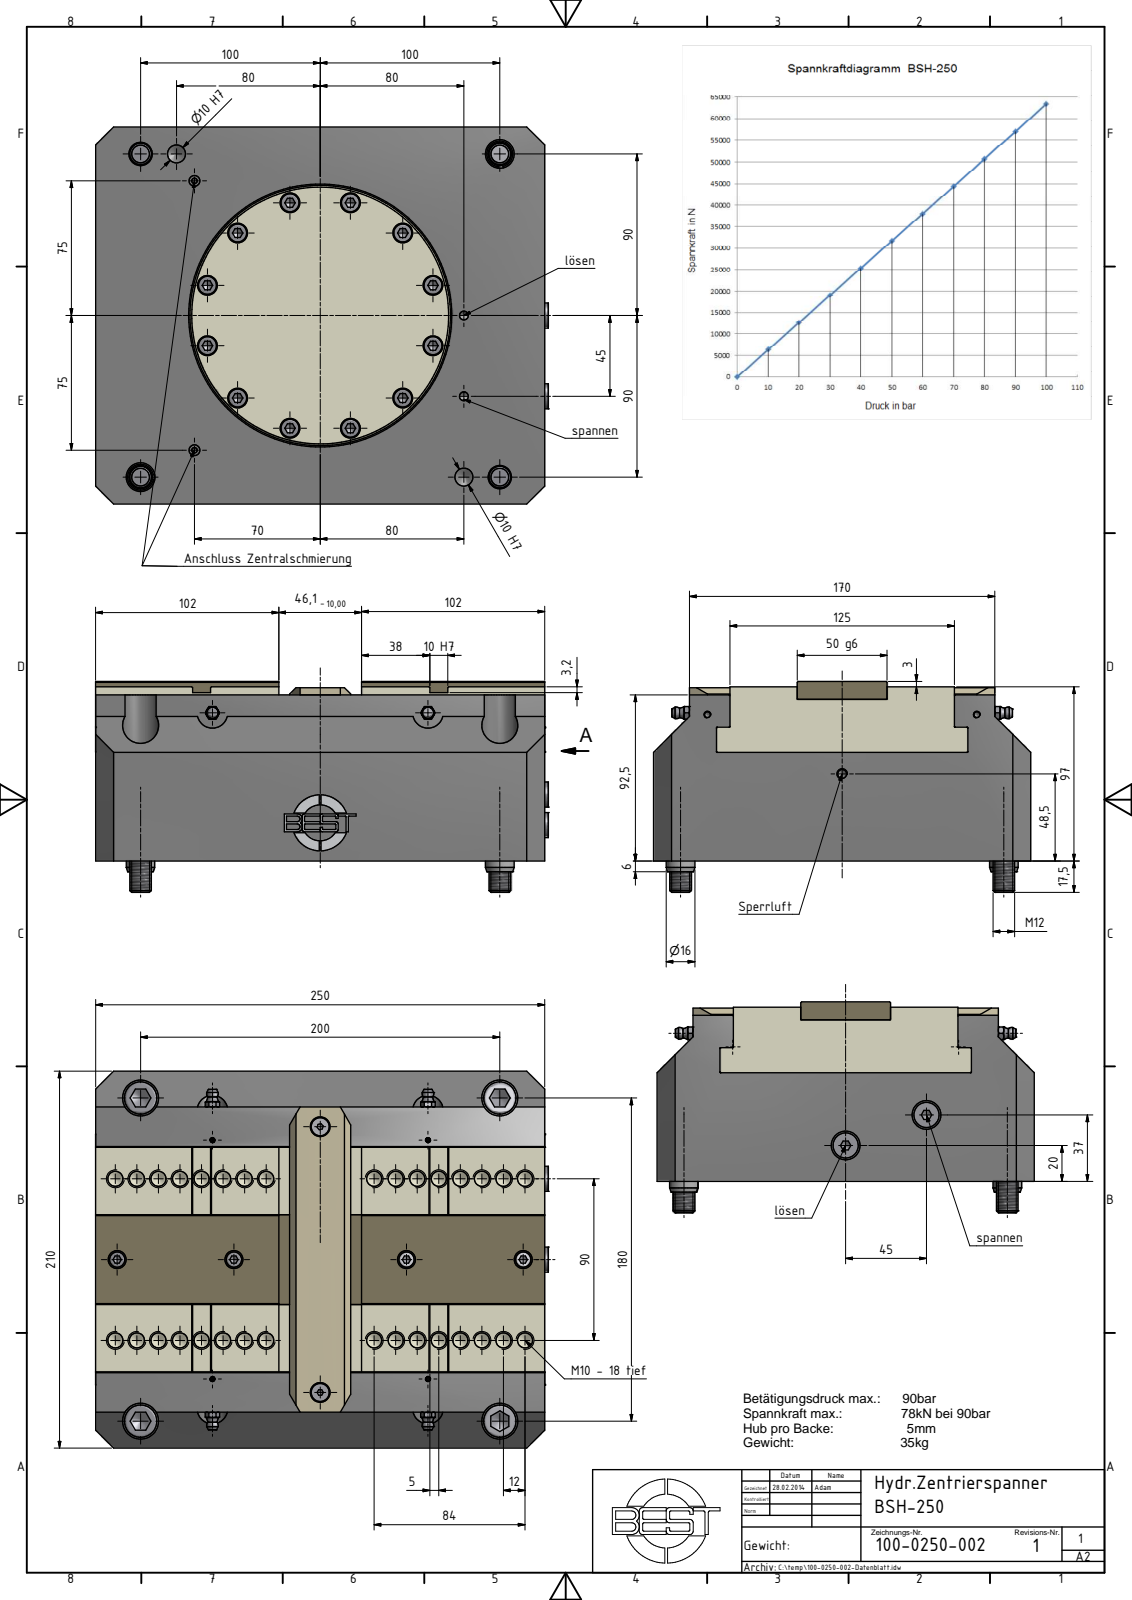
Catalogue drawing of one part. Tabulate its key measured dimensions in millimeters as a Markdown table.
| quantity | value |
| --- | --- |
| part name | 100-0250-002-Kd |
| STEP written by | Autodesk Inventor 2013 (AUTOMOTIVE_DESIGN) |
| units | millimeters |
| bodies | 1 solid, 634 faces (348 planar, 153 cylindrical, 133 other) |
| overall size | 252.54 × 210 × 117.5 |
| volume | 4 651 000 mm³ |
| surface area | 256 629 mm² |
| round holes (diameter × count) | 8.38 × 32, 4.92 × 5, 13 × 4, 16 × 4, 20 × 4, 3 × 2, 6 × 2, 8.57 × 2, 10 × 2 |
| round bosses / shafts (diameter × count) | 18 × 4, 12 × 4, 14 × 2, 3 × 2 |
| partial cylindrical surfaces (radius × count) | 0.5 × 18, 1.25 × 12, 1.56 × 4, 2.81 × 4, 0.1 × 2, 8.5 × 2, 10 × 1, 15.62 × 1 |
| main face-to-face distances | 210, 250, 92.5, 4.5, 97, 7.5, 3, 100, 250.04, 119 |
| hole center spacings | 12, 90.8, 24, 93.15, 36, 96.93, 48, 90 |
